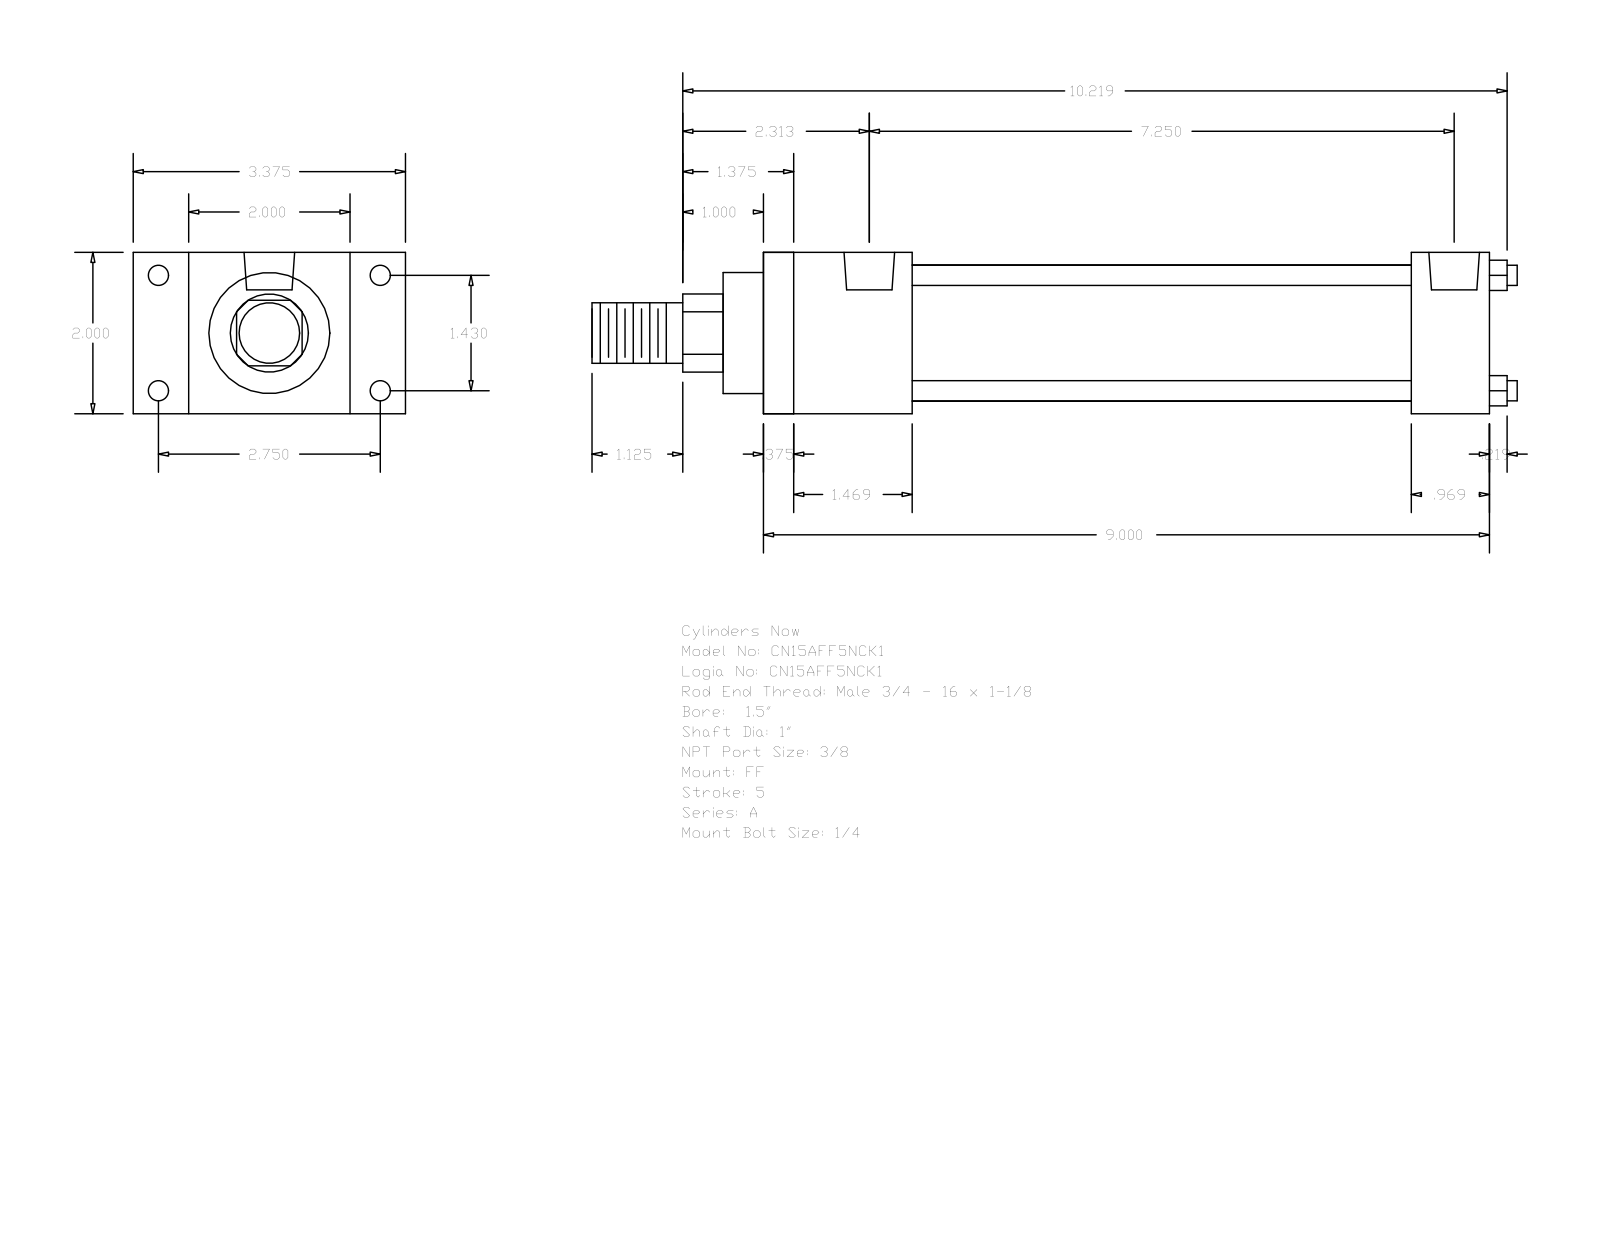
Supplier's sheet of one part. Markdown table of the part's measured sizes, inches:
| quantity | value |
| --- | --- |
| part name | A_FF__0150_1 |
| STEP written by | GSSL Pune (CONFIG_CONTROL_DESIGN) |
| units | inches |
| bodies | 0 solids, 92 faces (64 planar, 28 cylindrical, 0 other) |
| overall size | 11.469 × 3.375 × 2 |
| round holes (diameter × count) | 0.219 × 4, 0.25 × 4, 0.627 × 2 |
| round bosses / shafts (diameter × count) | 0.25 × 4, 1.69 × 1, 1.5 × 1, 1 × 1, 0.75 × 1 |
| partial cylindrical surfaces (radius × count) | 0.484 × 1 |
| main face-to-face distances | 2, 9, 0.375, 8.625, 1.844, 8.031, 1.469, 7.656, 6.187, 7.156 |
| hole center spacings | 0.156, 1.43, 2.75, 3.099, 6.937, 7.094, 7.25 |
